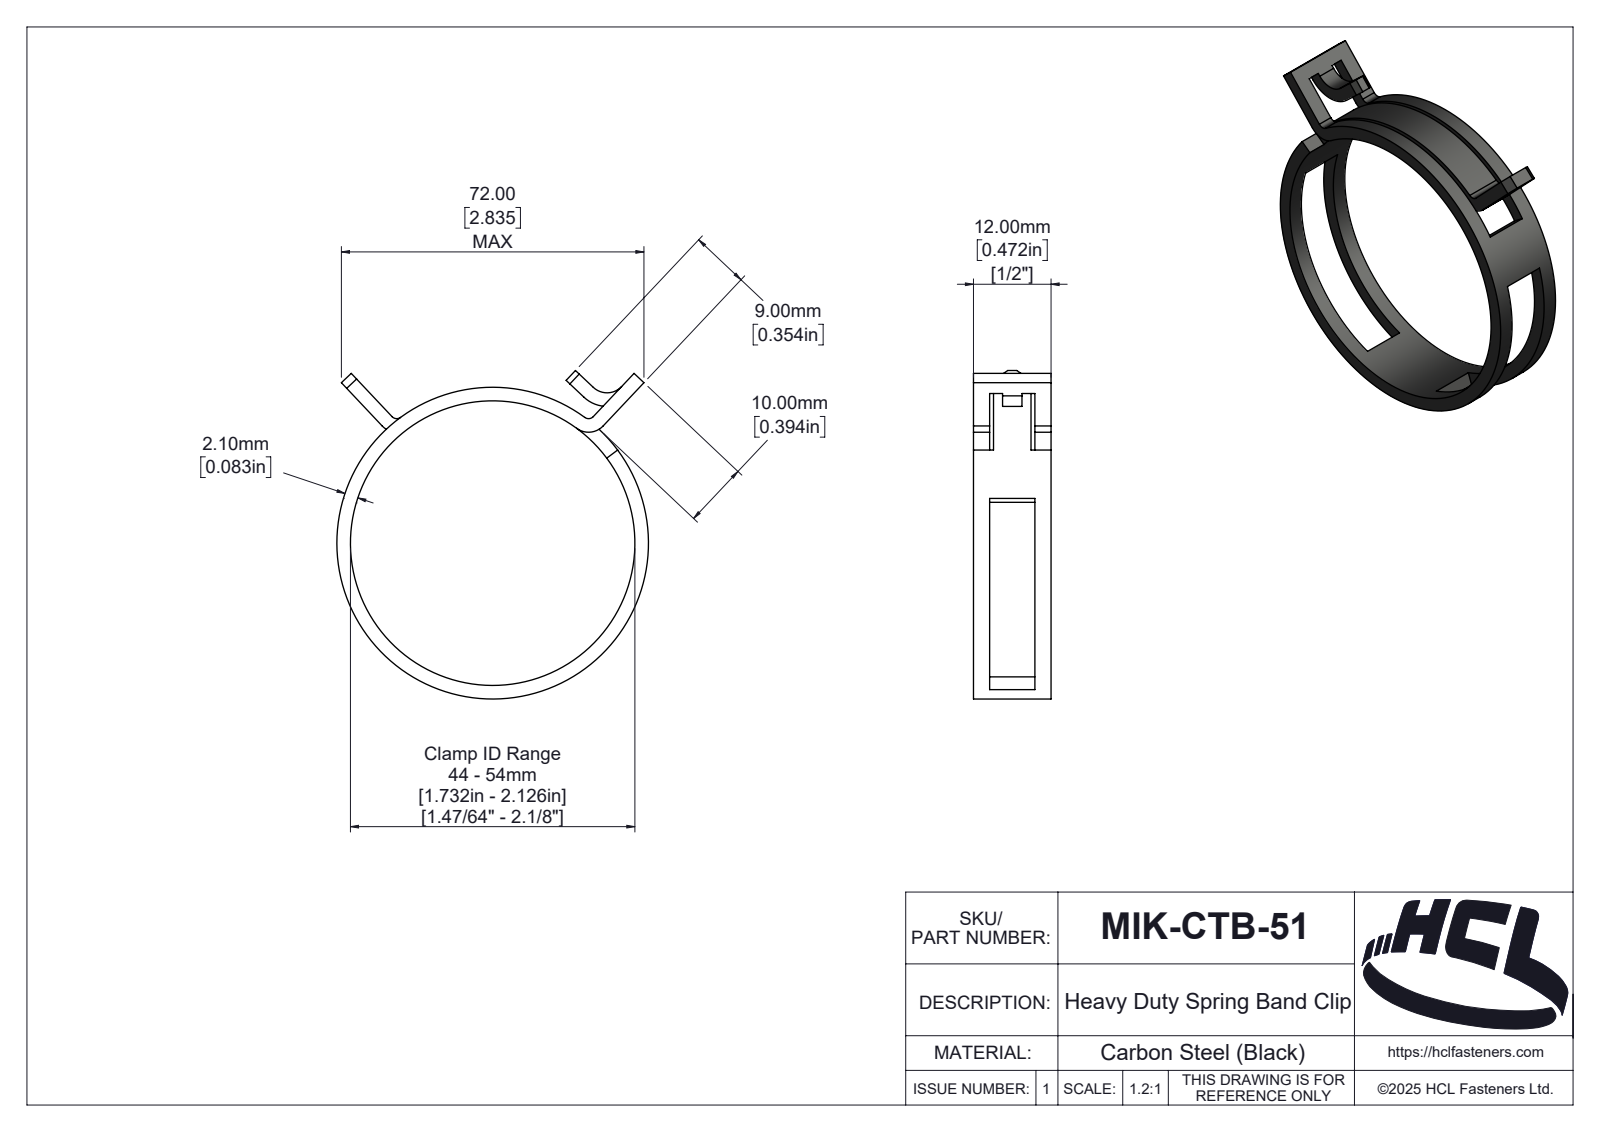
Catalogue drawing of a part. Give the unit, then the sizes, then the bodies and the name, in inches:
Units: inches
Overall size (bounding box): 2 × 1.898 × 0.472
Round holes (diameter × count): ⌀1.732 ×1
Round bosses / shafts (diameter × count): ⌀1.898 ×1
Partial cylindrical surfaces — rounded edges, fillets, slot ends (radius × count): R0.122 ×3, R0.039 ×2, R0.013 ×1, R0.053 ×1, R0.066 ×1, R0.07 ×1, R0.084 ×1, R0.119 ×1
Main face-to-face distances: 0.098, 0.374, 0.472, 0.276, 0.122, 0.35, 0.024, 0.252, 0.083, 0.228
Volume: 0.167 in³ · Surface area: 6.366 in²
Bodies: 1 solid, 149 faces (36 planar, 64 cylindrical, 49 other)
Part name (STEP PRODUCT): MIK-CTB-51
STEP written by: SolidWorks 2025 (AUTOMOTIVE_DESIGN)
